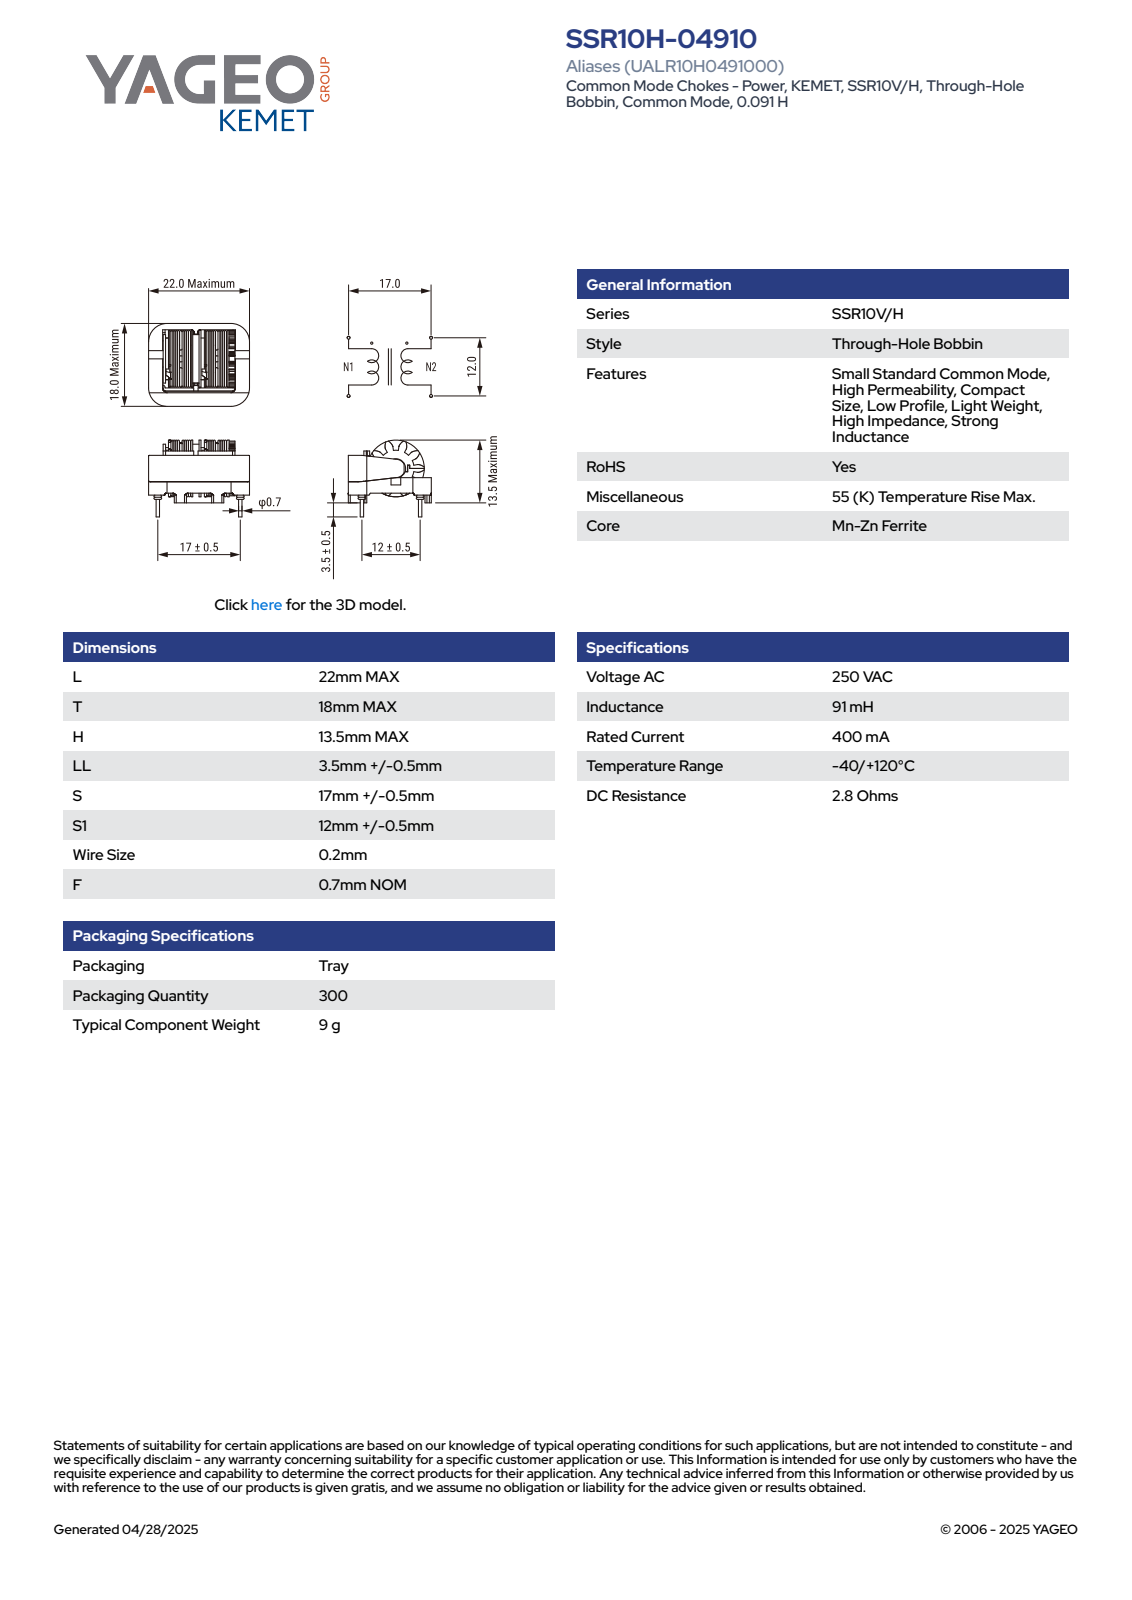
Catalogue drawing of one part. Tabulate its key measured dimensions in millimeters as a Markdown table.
| quantity | value |
| --- | --- |
| part name | SSR10H(MAX-LOGO) |
| STEP written by | SolidWorks 2018 (AUTOMOTIVE_DESIGN) |
| units | millimeters |
| bodies | 1 solid, 371 faces (218 planar, 117 cylindrical, 36 other) |
| overall size | 22 × 18 × 17 |
| volume | 2 571 mm³ |
| surface area | 3 348 mm² |
| round holes (diameter × count) | 4 × 1 |
| round bosses / shafts (diameter × count) | 0.7 × 4, 11.7 × 1, 10 × 1, 8.6 × 1, 5.7 × 1 |
| partial cylindrical surfaces (radius × count) | 1.46 × 20, 0.5 × 15, 0.4 × 8, 0.1 × 6, 3.8 × 6, 1 × 3, 0.2 × 2, 0.15 × 1 |
| main face-to-face distances | 0.4, 12, 1.7, 7.4, 0.6, 1.6, 4.6, 11.5, 0.5, 5.8 |
